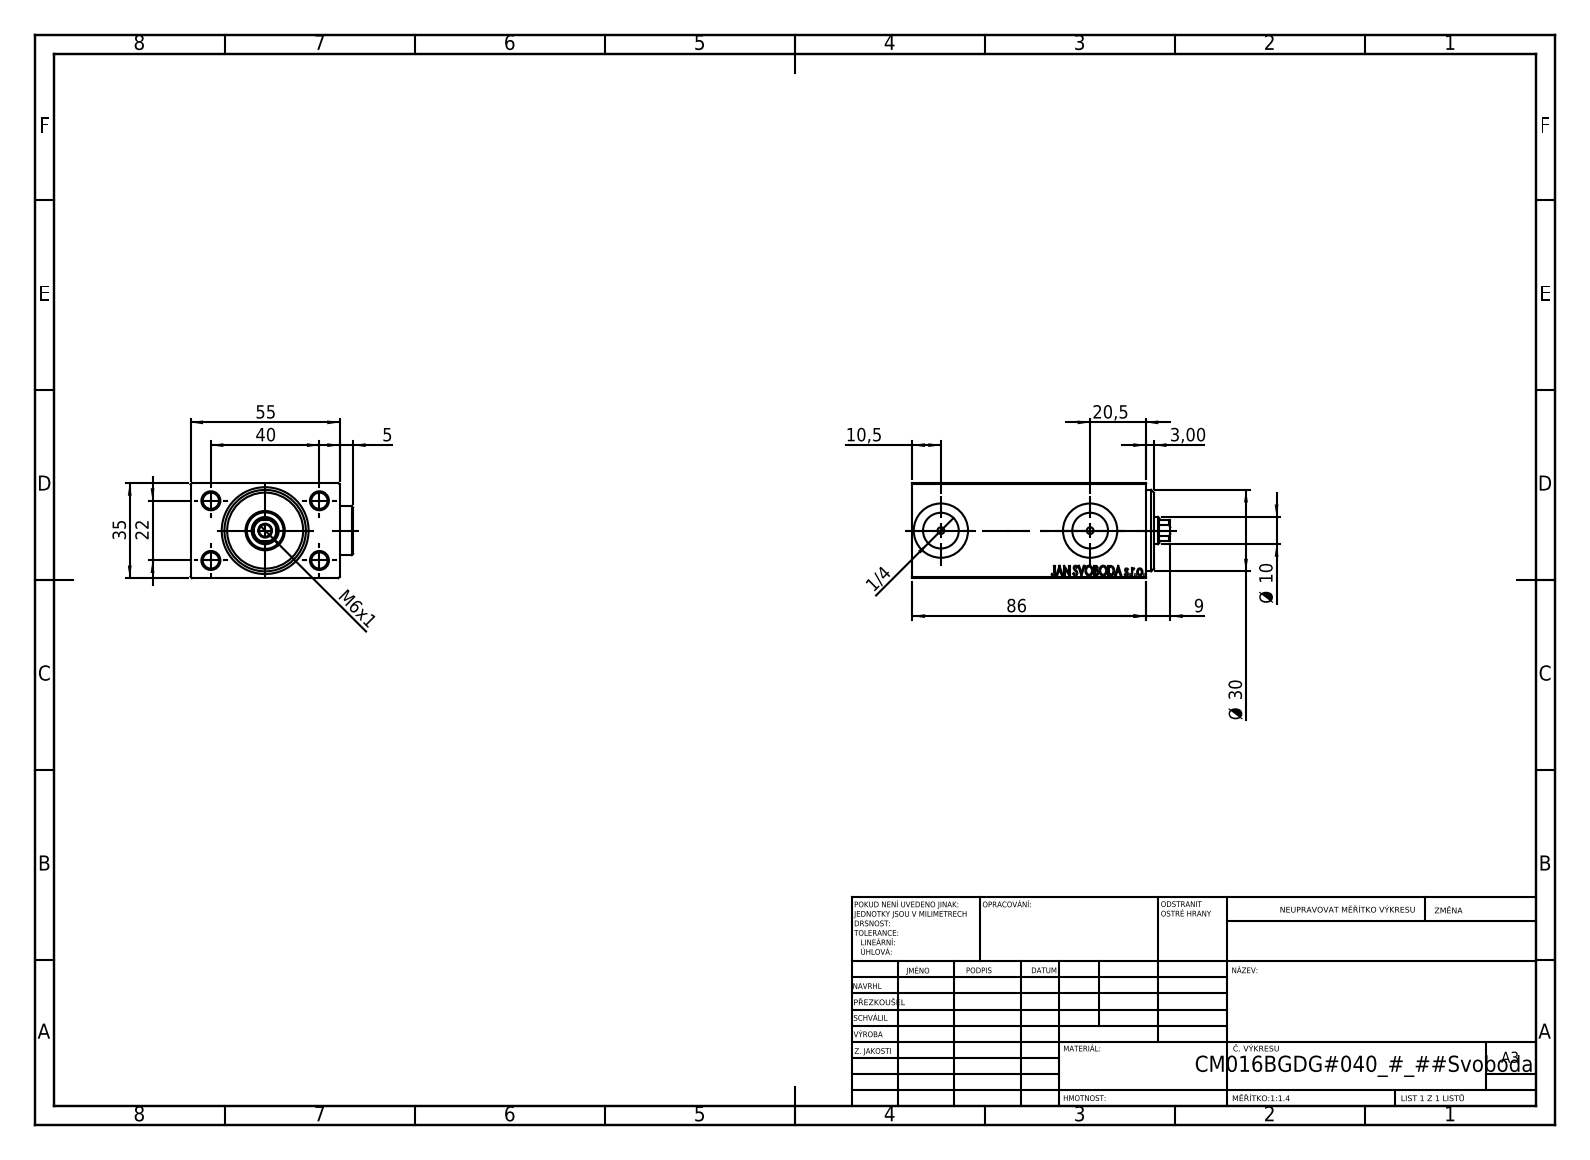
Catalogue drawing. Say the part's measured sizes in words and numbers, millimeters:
The part is named "V450CM_B_VCP; Zatka_OIL_PORT; V450CM_VC_B; V450CM_B_Body". Its 3-D file was written by "SolidWorks 2019 (CONFIG_CONTROL_DESIGN)". It is 5 solids with 935 faces: 435 planar, 70 cylindrical and 430 other. Overall it measures 95 by 59.9 by 35 millimeters. Its volume is 155 285 cubic millimeters and its surface area 35 688 square millimeters. Round holes: 4 of diameter 6, 2 of diameter 2.5, 2 of diameter 13.16, 2 of diameter 20, 1 of diameter 4.5, 1 of diameter 10, 1 of diameter 13.5, 1 of diameter 14.5, 1 of diameter 16, 1 of diameter 18, 1 of diameter 30. Round bosses or shafts: 2 of diameter 18. Partial cylindrical surfaces (rounded edges, fillets, slot ends): 1 of radius 4.5. The main face-to-face distances are 35, 55, 5, 81, 54.9, 86, 3, 8, 89, 54.8. The hole center spacings are 22.83, 22, 40, 45.65, 55.
